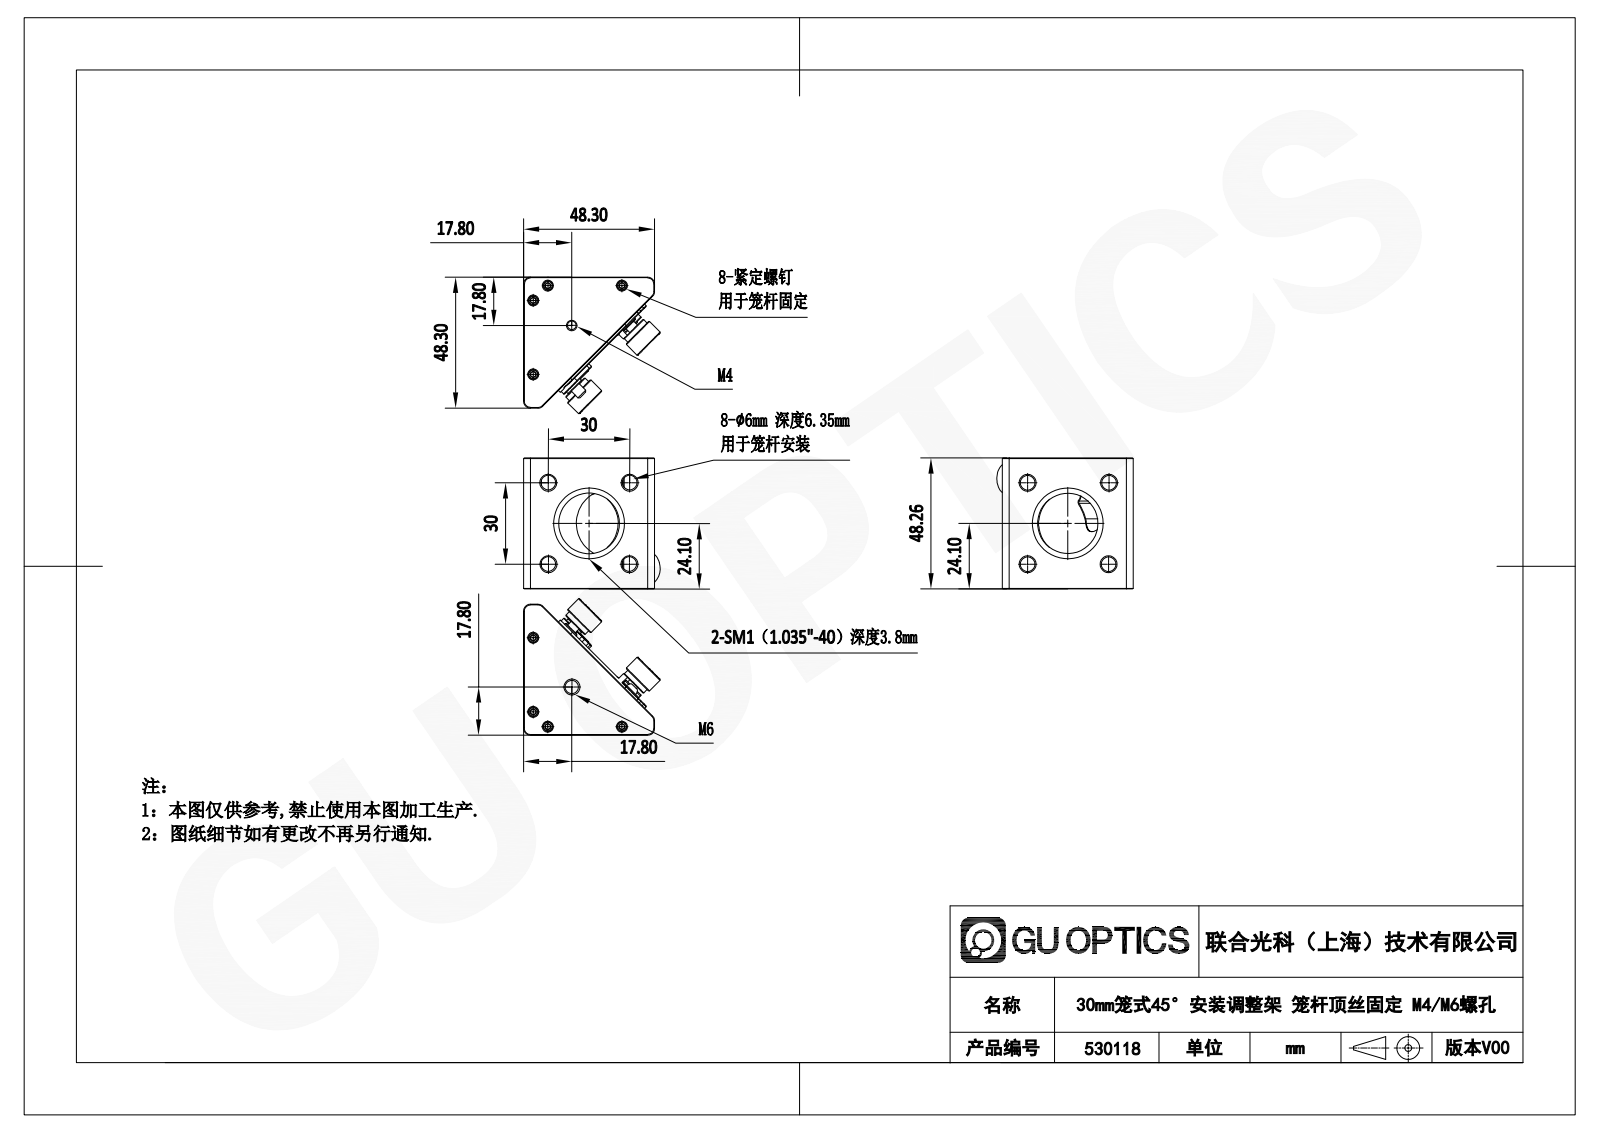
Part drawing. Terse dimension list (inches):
name: 530118
written by: SolidWorks 2020 (CONFIG_CONTROL_DESIGN)
unit: in
bodies: 40 solids, 704 faces (356 planar, 189 cylindrical, 159 other)
size: 2.127 × 2.127 × 1.9
volume: 2.907 in³; area: 43.31 in²
holes: 6× ⌀0.236, 5× ⌀0.13, 4× ⌀0.25, 3× ⌀0.114, 3× ⌀0.118, 3× ⌀0.138, 3× ⌀0.14, 3× ⌀0.146, 3× ⌀0.148, 3× ⌀0.276, 2× ⌀0.063, 2× ⌀0.094
bosses: 7× ⌀0.157, 5× ⌀0.059, 3× ⌀0.472, 3× ⌀0.394, 3× ⌀0.079, 2× ⌀0.268, 2× ⌀0.236, 2× ⌀0.217
rounds: 30× R0.031, 7× R0.039, 6× R0.037, 5× R0.1, 4× R0.031, 4× R0.05, 4× R0.17, 4× R0.25
face distances: 0.045, 1.9, 0.163, 0.118, 0.398, 0.28, 0.235, 0.068, 0.33, 0.212
hole spacings: 1.181, 0.835, 1.3, 1.453, 1.67, 0.215, 0.991, 1.2
